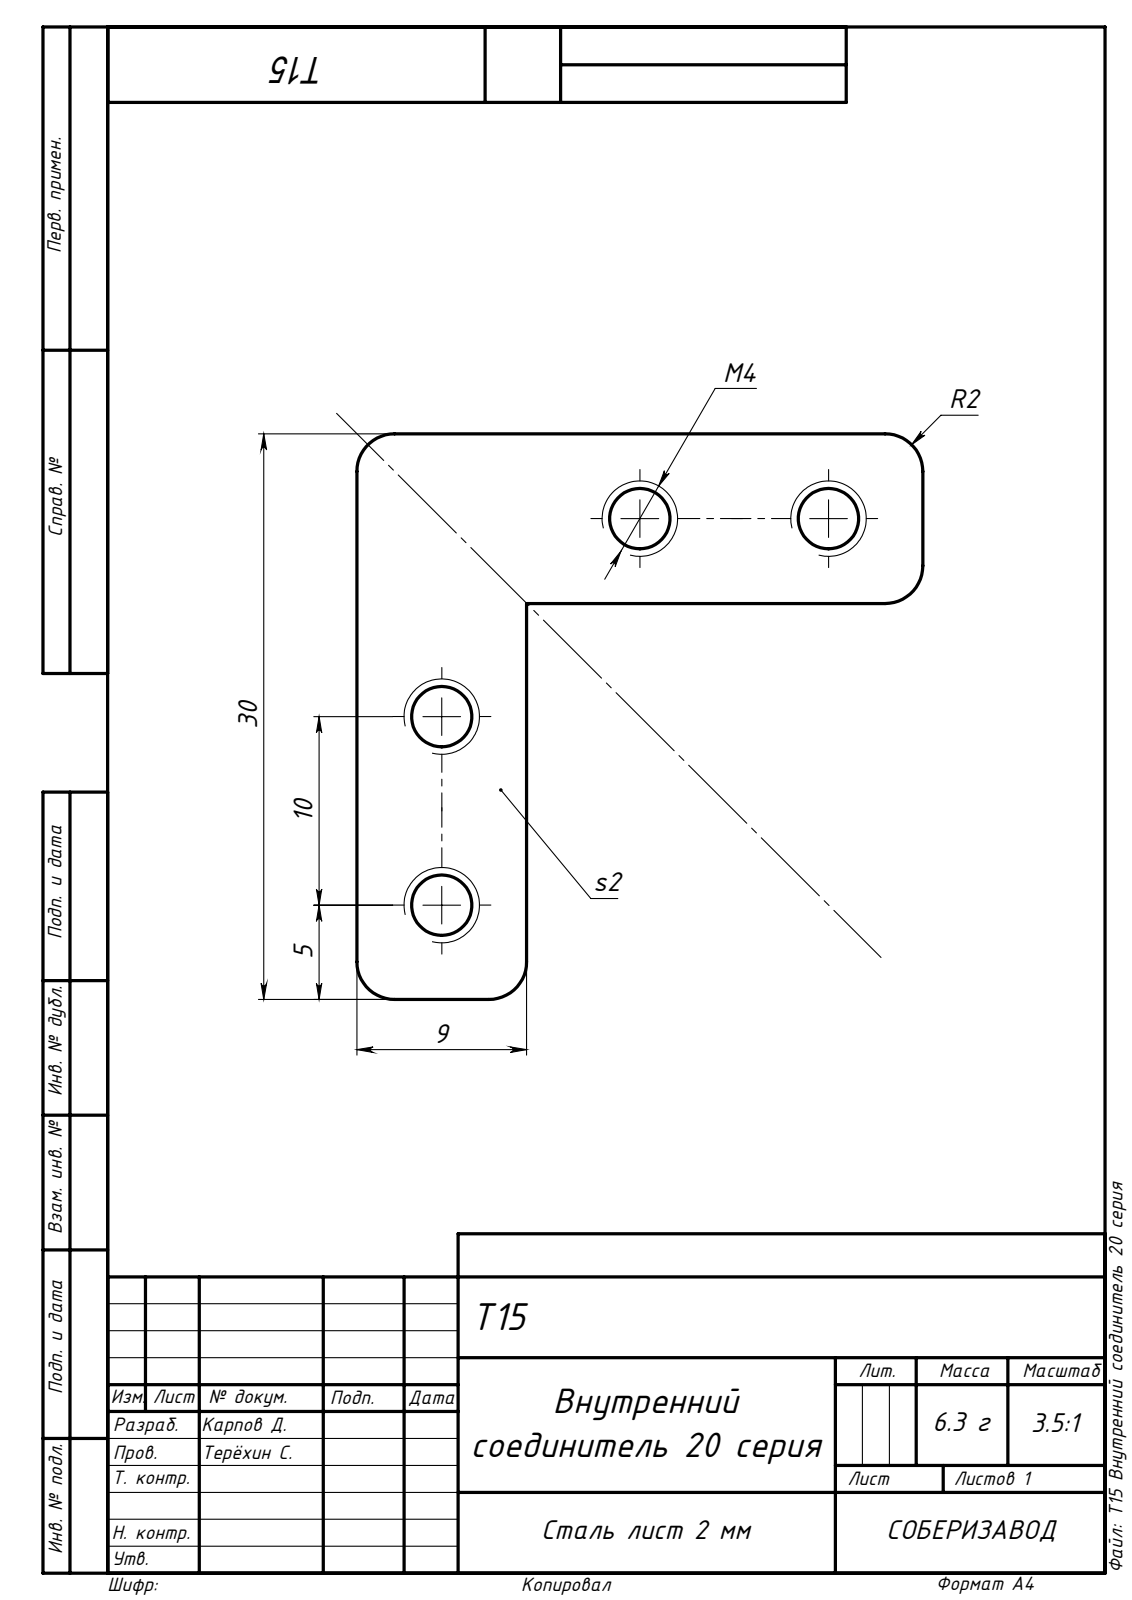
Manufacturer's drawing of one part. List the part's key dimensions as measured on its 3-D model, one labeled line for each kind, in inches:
Part name (STEP PRODUCT): T15 Внутренний соединитель 20 серия
STEP written by: SolidWorks 2021 (AUTOMOTIVE_DESIGN)
Units: inches
Bodies: 1 solid, 21 faces (8 planar, 13 cylindrical, 0 other)
Overall size (bounding box): 1.181 × 1.181 × 0.079
Volume: 0.052 in³ · Surface area: 1.793 in²
Round holes (diameter × count): ⌀0.126 ×4
Partial cylindrical surfaces — rounded edges, fillets, slot ends (radius × count): R0.079 ×5
Main face-to-face distances: 0.079, 0.354, 1.181, 0.827
Hole centre spacings: 0.394, 0.907, 0.585, 1.141
